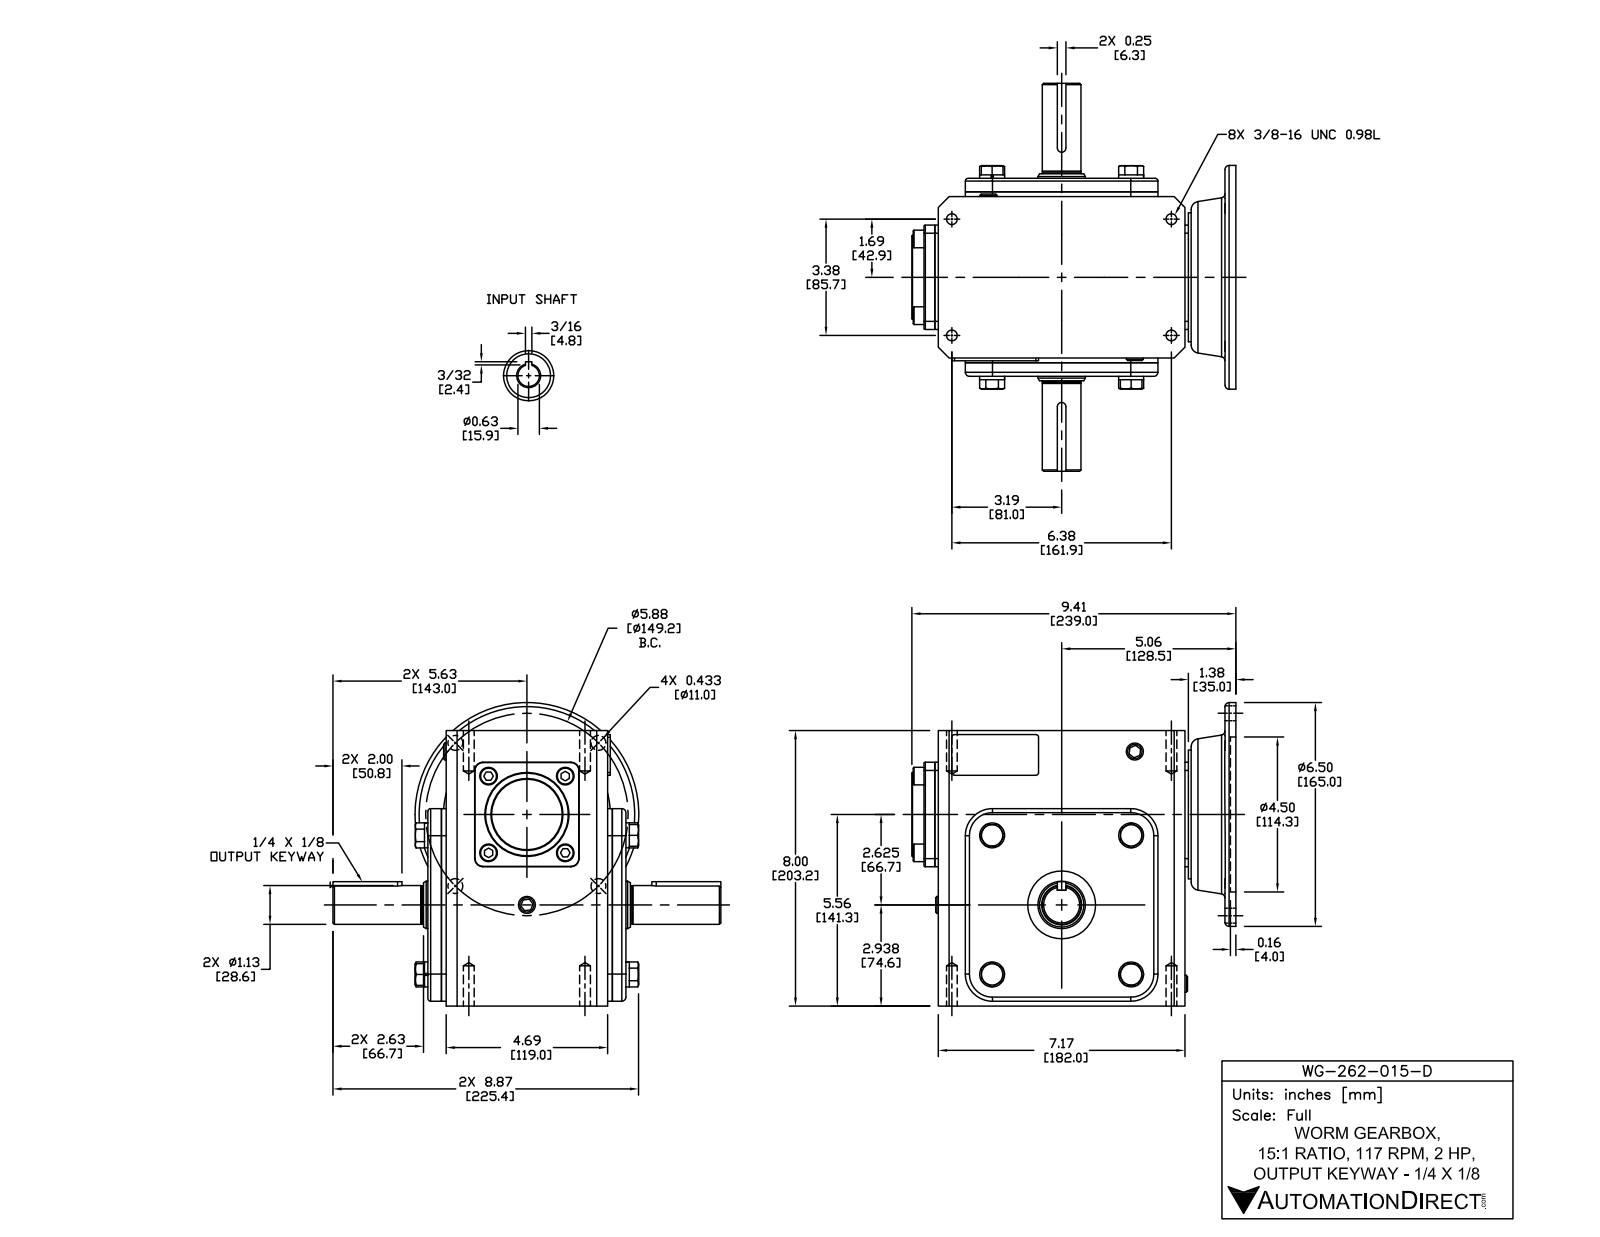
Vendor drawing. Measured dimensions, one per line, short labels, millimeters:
name: WG-262-015-D
written by: SolidWorks 2015 (CONFIG_CONTROL_DESIGN)
unit: mm
bodies: 39 solids, 562 faces (307 planar, 150 cylindrical, 105 other)
size: 286 × 239 × 223.8
volume: 5 278 000 mm³; area: 408 100 mm²
holes: 4× ⌀8, 4× ⌀10.3, 1× ⌀15, 1× ⌀15.9, 1× ⌀30, 1× ⌀35, 1× ⌀37, 1× ⌀50, 1× ⌀97, 1× ⌀114.3
bosses: 4× ⌀18.4, 4× ⌀13, 1× ⌀165, 1× ⌀62, 1× ⌀52, 1× ⌀29, 1× ⌀28.6, 1× ⌀28.3
rounds: 8× R2, 8× R3, 4× R6, 4× R20, 2× R0.5, 2× R1, 2× R3.2
face distances: 126, 10, 136, 132.5, 13.5, 3.5, 122.5, 203.2, 2.5, 184.5
hole spacings: 74.6, 105.5, 54.6, 85.7, 130.6, 149.2, 161.9, 183.2
